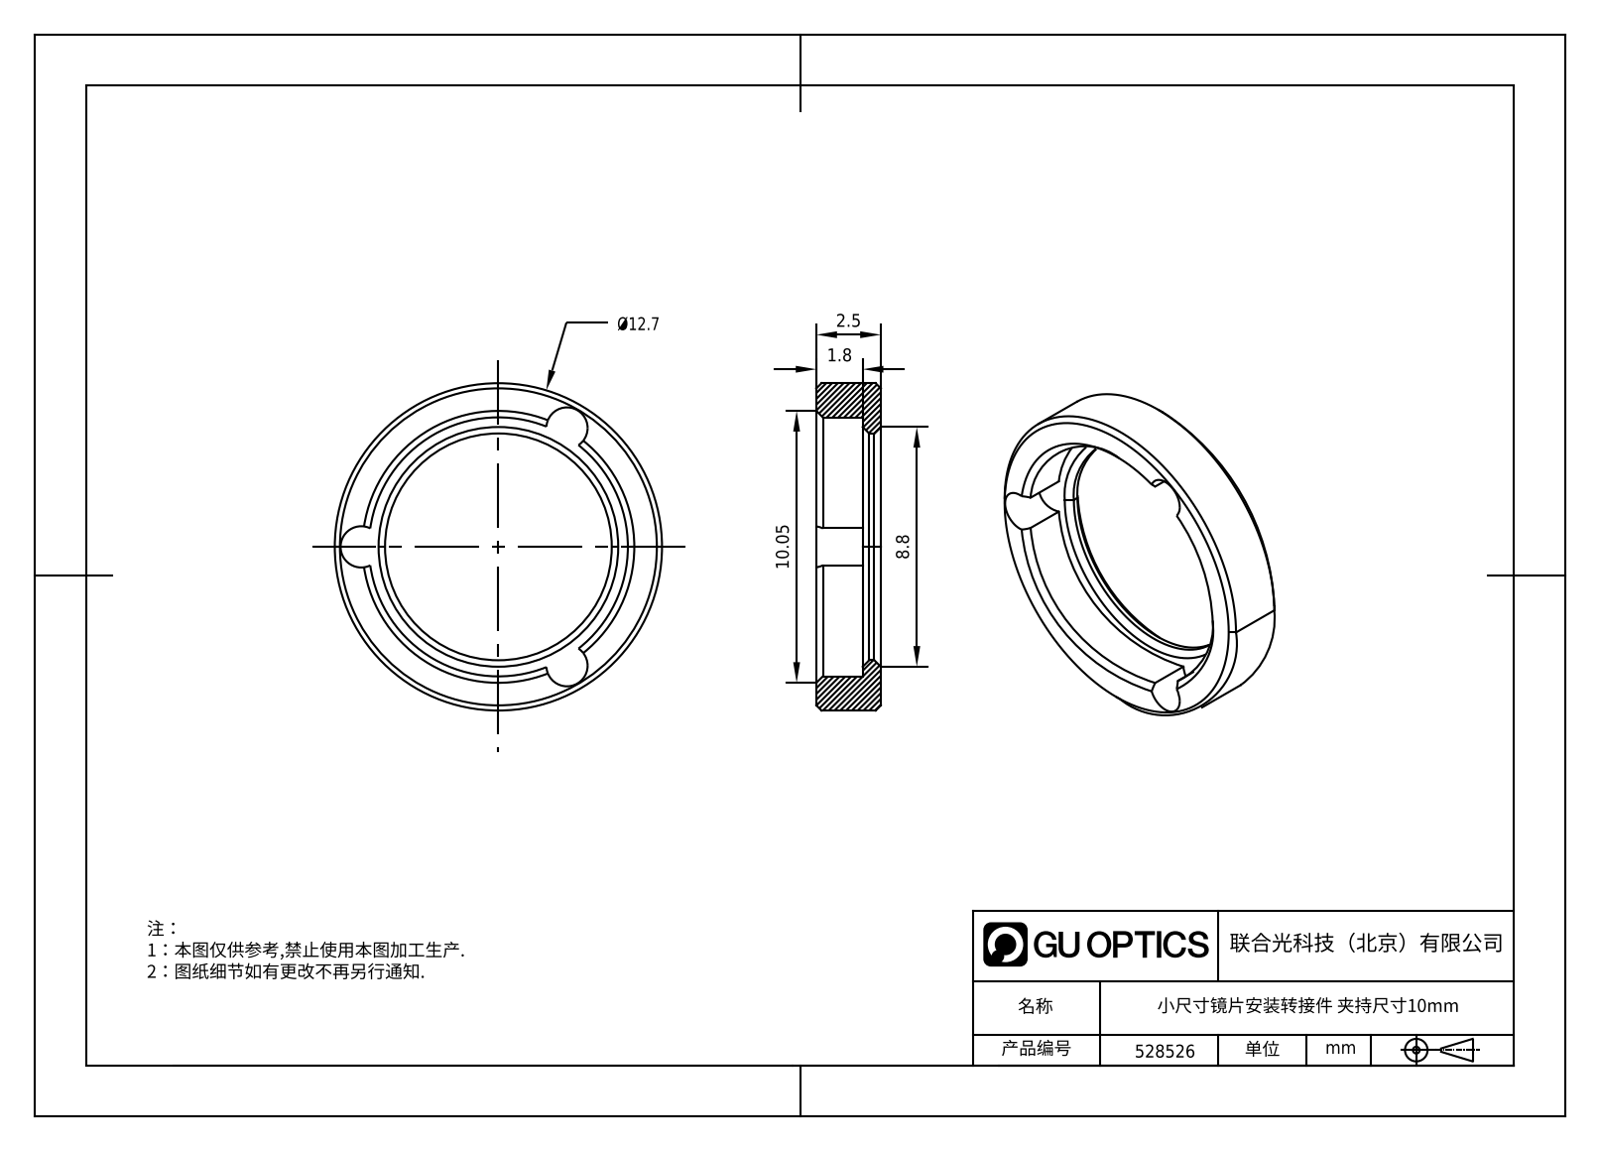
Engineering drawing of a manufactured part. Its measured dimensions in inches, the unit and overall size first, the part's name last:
Units: inches
Overall size (bounding box): 0.5 × 0.5 × 0.098
Round holes (diameter × count): ⌀0.346 ×1, ⌀0.396 ×1
Round bosses / shafts (diameter × count): ⌀0.5 ×1
Partial cylindrical surfaces — rounded edges, fillets, slot ends (radius × count): R0.031 ×3
Main face-to-face distances: 0.098, 0.028, 0.071
Volume: 0.007 in³ · Surface area: 0.459 in²
Bodies: 1 solid, 28 faces (3 planar, 13 cylindrical, 12 other)
Part name (STEP PRODUCT): 1.6.4.12-ZSJ-05-10
STEP written by: SolidWorks 2021 (CONFIG_CONTROL_DESIGN)
